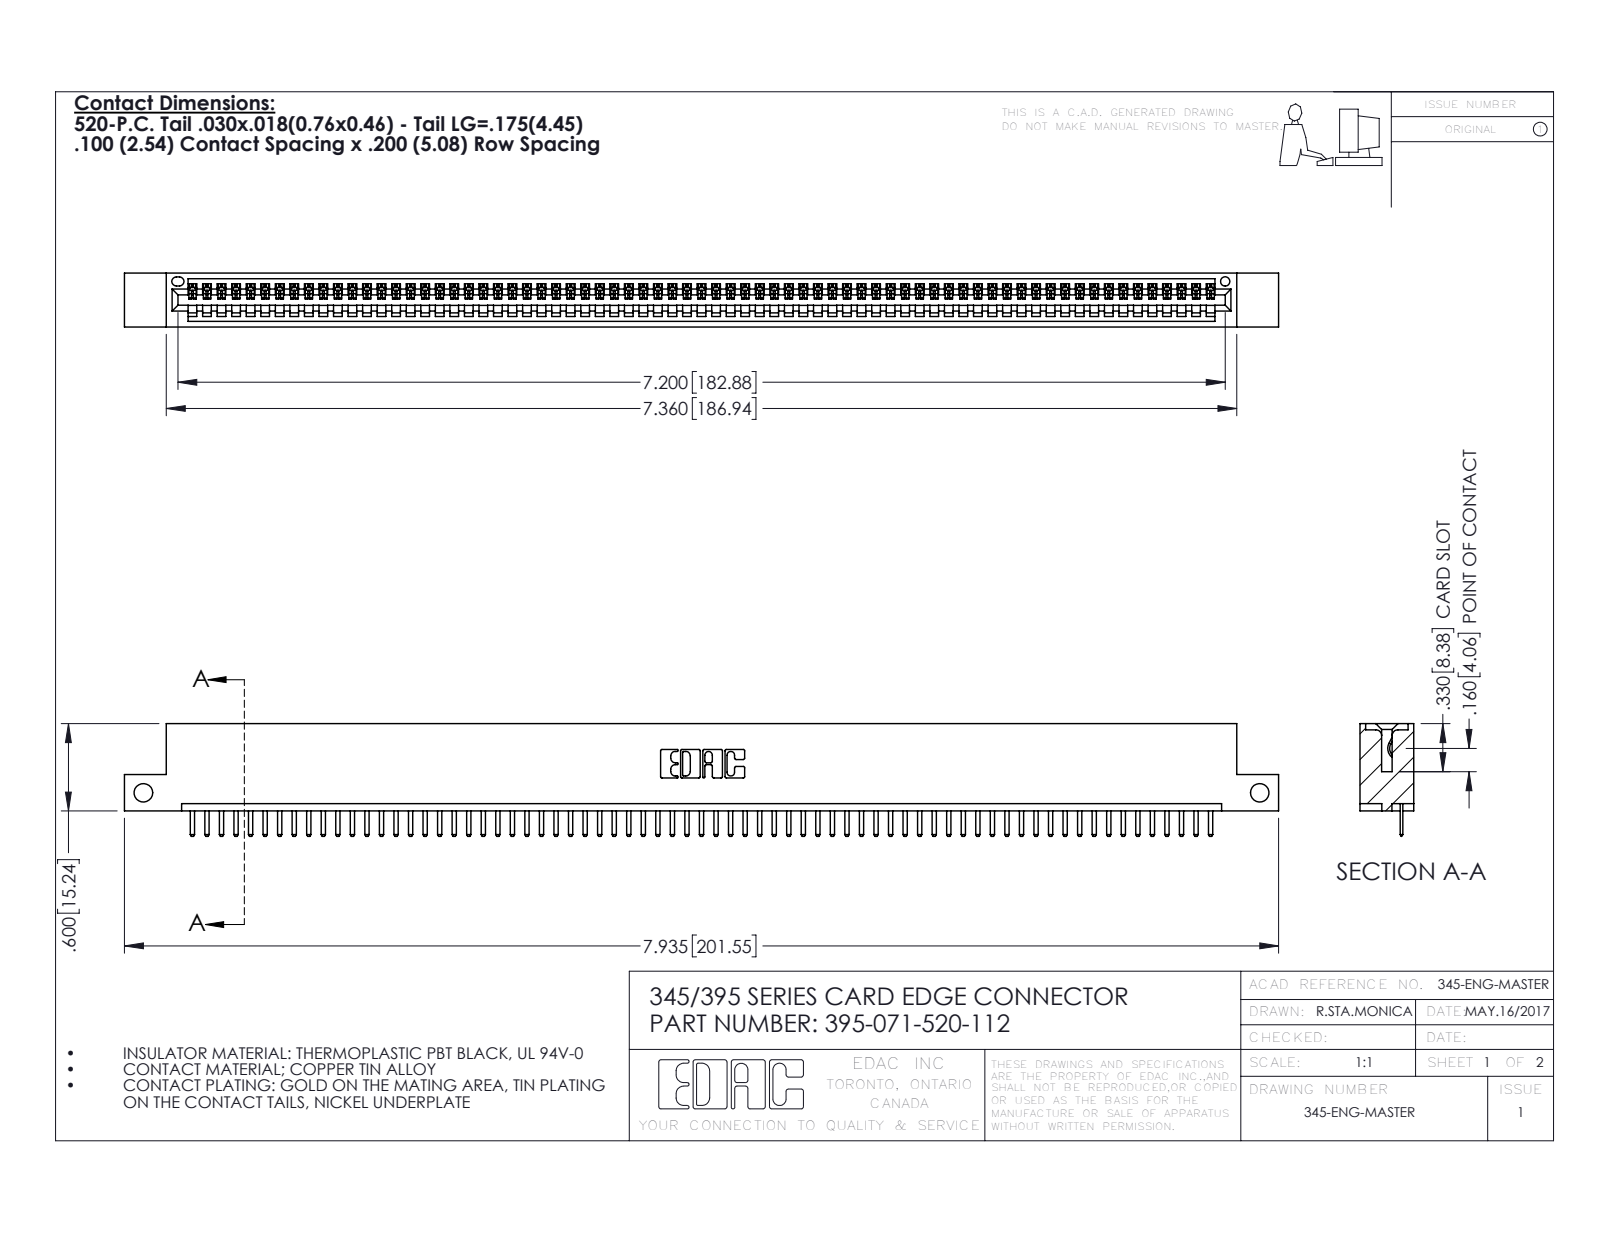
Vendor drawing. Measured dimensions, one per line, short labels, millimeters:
name: 345-292-001_345-293-120; 345 Part_Flush Mounting Lugs - Side Mount; 395-071-520-112
written by: SolidWorks 2016 (CONFIG_CONTROL_DESIGN)
unit: mm
bodies: 72 solids, 4528 faces (3062 planar, 1466 cylindrical, 0 other)
size: 201.5 × 19.7 × 9.4
volume: 19 090 mm³; area: 24 950 mm²
holes: 2× ⌀3.3, 1× ⌀1.6
rounds: 144× R0.3, 142× R0.2, 22× R0.3, 6× R0.2, 6× R0.8, 3× R0.7, 2× R0.8, 2× R1
face distances: 7.6, 1.8, 9.4, 5.1, 2.5, 6.9, 0.6, 5.7, 1.8, 3.8
hole spacings: 194.9
